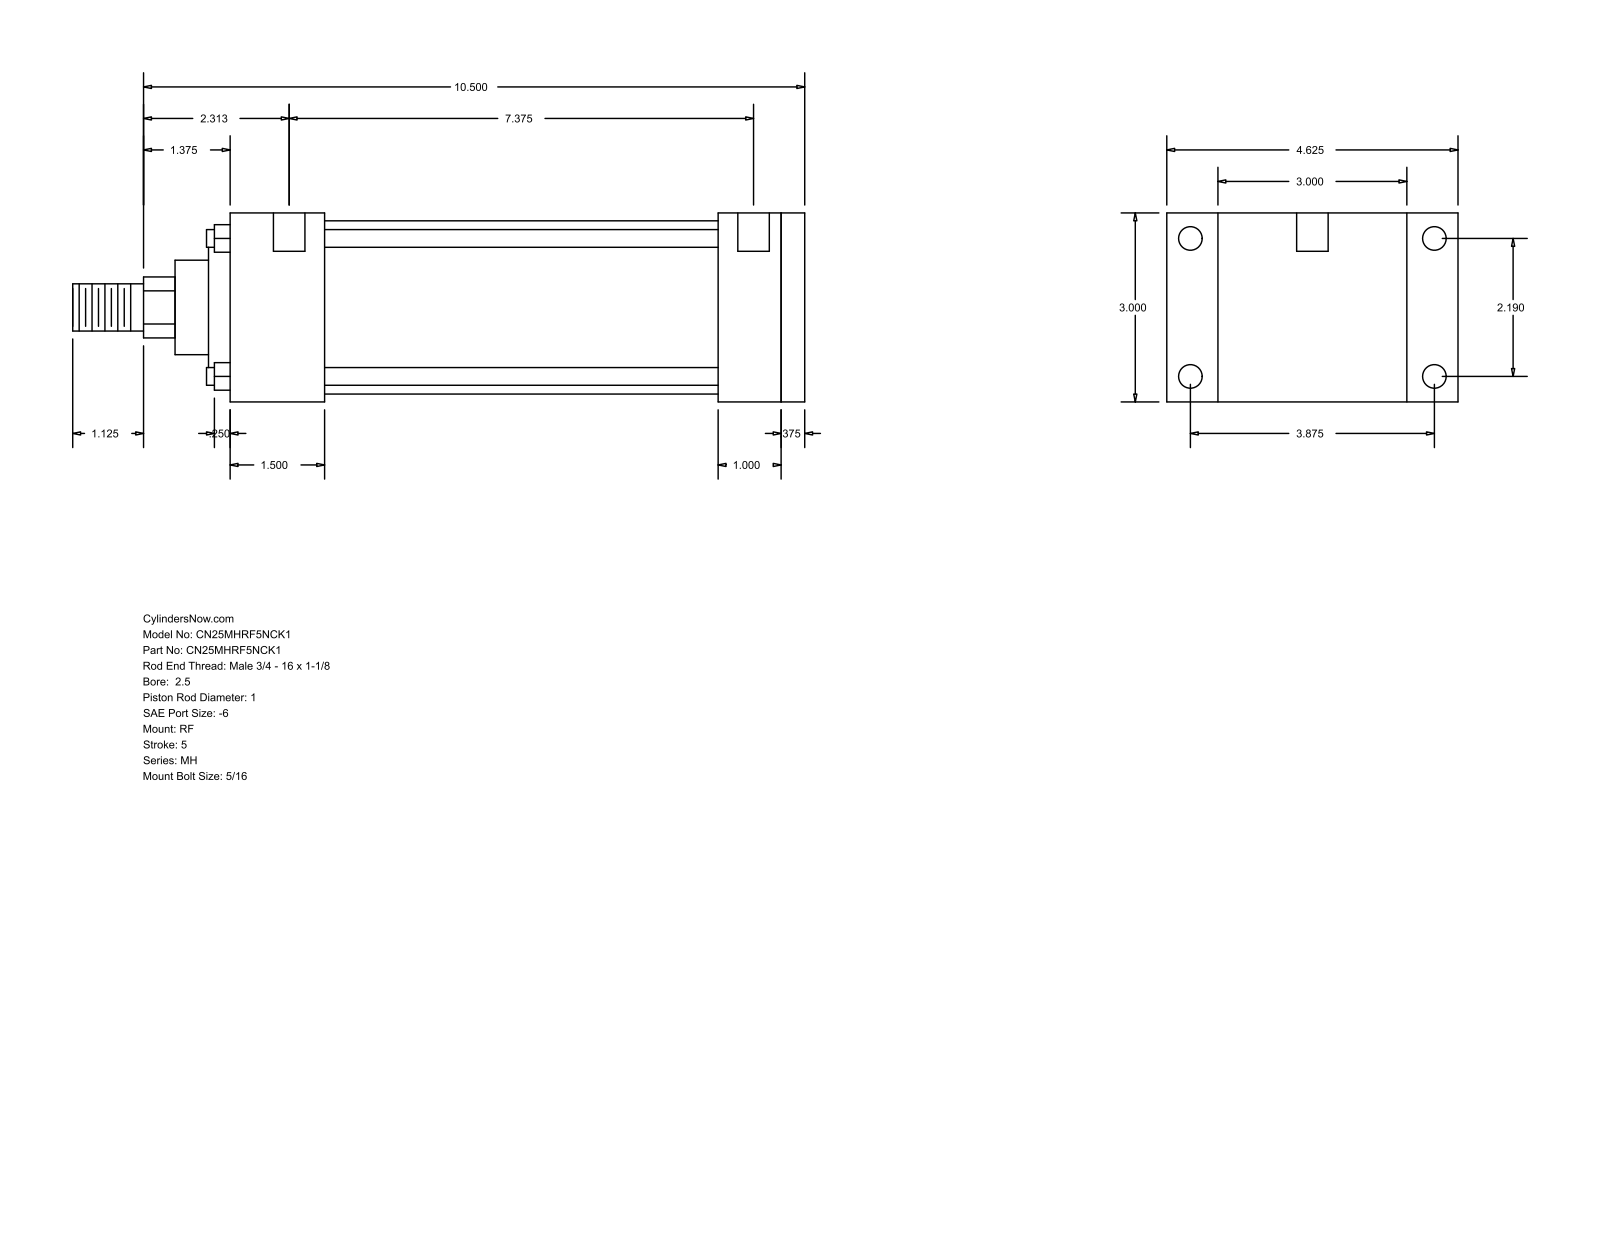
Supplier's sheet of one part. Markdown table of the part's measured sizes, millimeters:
| quantity | value |
| --- | --- |
| part name | MH_RF__0250_1 |
| STEP written by | GSSL Pune (CONFIG_CONTROL_DESIGN) |
| units | millimeters |
| bodies | 0 solids, 94 faces (65 planar, 29 cylindrical, 0 other) |
| overall size | 295.27 × 117.47 × 76.2 |
| round holes (diameter × count) | 5.56 × 4, 9.53 × 4, 12.7 × 2 |
| round bosses / shafts (diameter × count) | 7.14 × 4, 69.85 × 1, 60.33 × 1, 38.1 × 1, 25.4 × 1, 19.05 × 1 |
| partial cylindrical surfaces (radius × count) | 12.29 × 1 |
| main face-to-face distances | 76.2, 9.52, 231.78, 222.26, 25.4, 34.92, 196.86, 38.11, 158.75, 184.15 |
| hole center spacings | 55.62, 98.42, 113.05, 195.26, 3.18, 4.76, 187.32, 190.5 |
